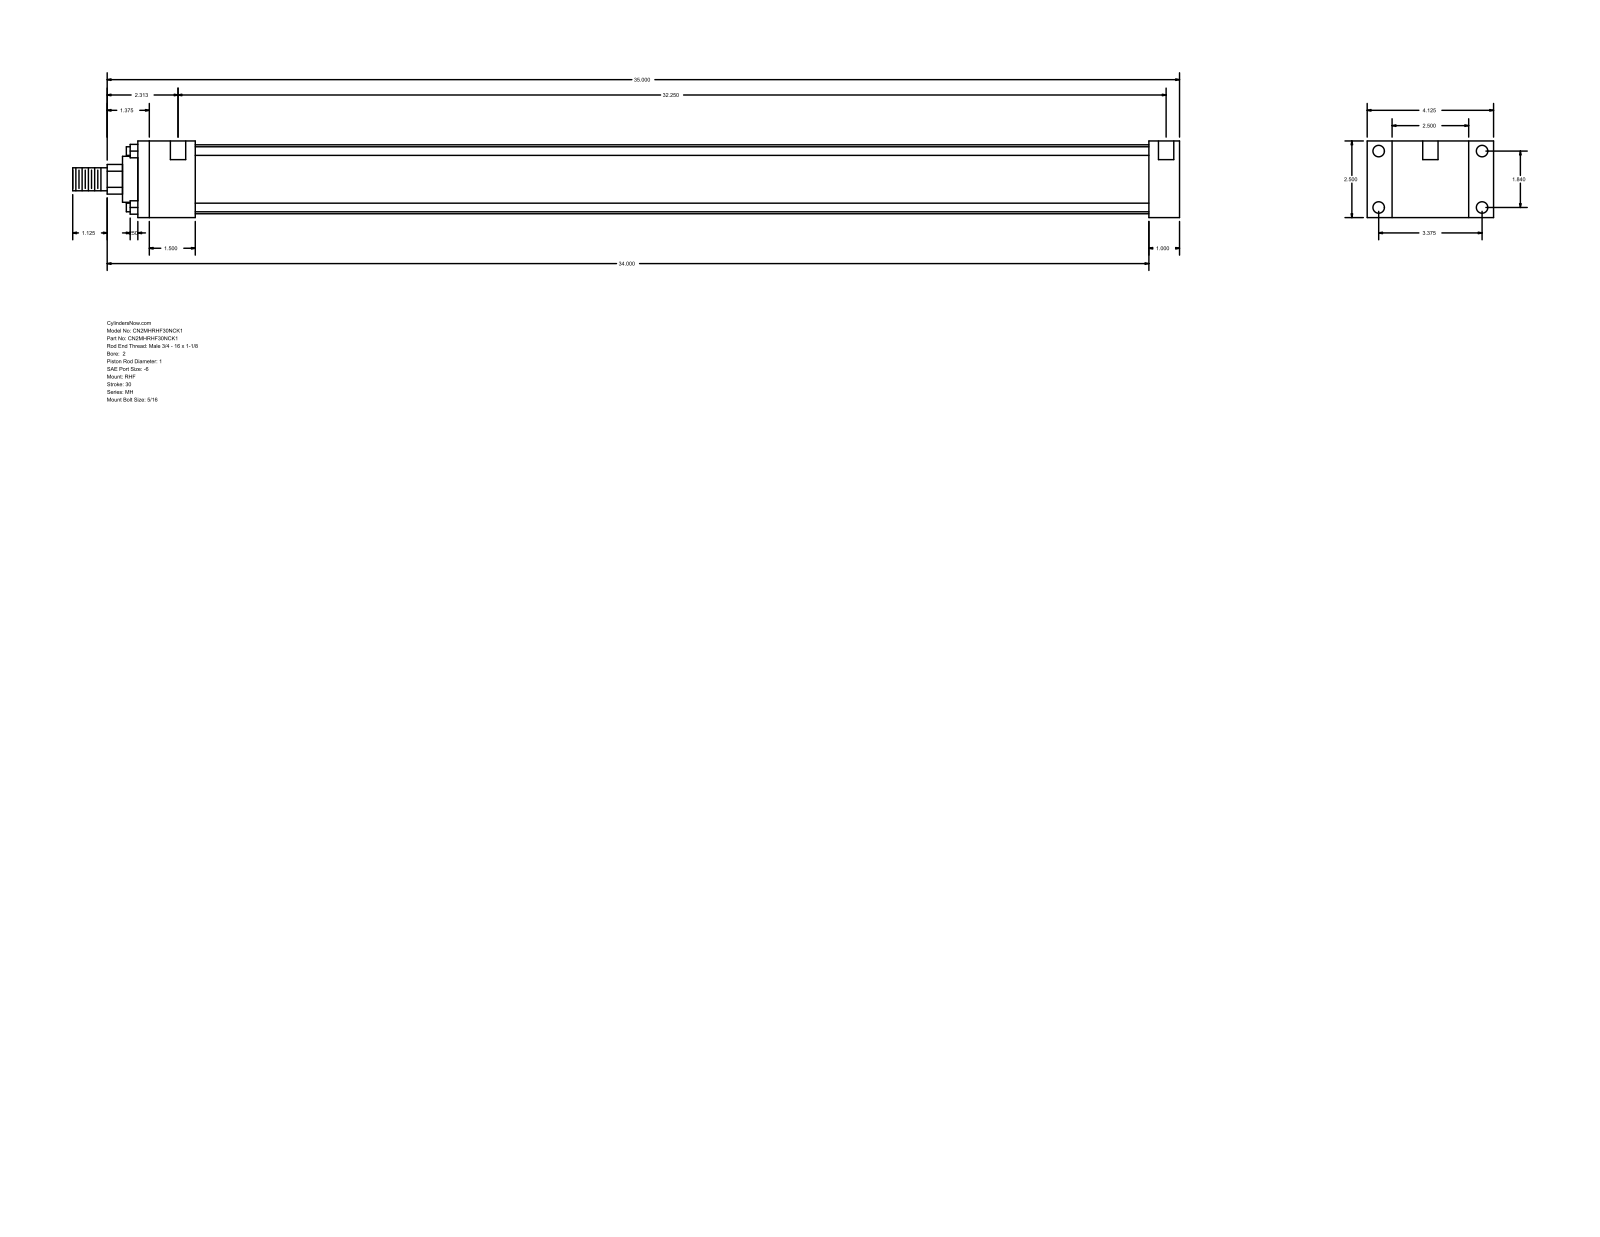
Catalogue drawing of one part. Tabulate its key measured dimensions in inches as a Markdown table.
| quantity | value |
| --- | --- |
| part name | MH_RHF__0200_1 |
| STEP written by | GSSL Pune (CONFIG_CONTROL_DESIGN) |
| units | inches |
| bodies | 0 solids, 88 faces (60 planar, 28 cylindrical, 0 other) |
| overall size | 36.125 × 4.125 × 2.5 |
| round holes (diameter × count) | 0.219 × 4, 0.375 × 4, 0.5 × 2 |
| round bosses / shafts (diameter × count) | 0.281 × 4, 2.25 × 1, 1.5 × 1, 1 × 1, 0.75 × 1 |
| partial cylindrical surfaces (radius × count) | 0.484 × 1 |
| main face-to-face distances | 2.5, 1, 0.813, 3.313, 34, 33, 4.125, 1.875, 31.125, 32.125 |
| hole center spacings | 1.84, 3.375, 3.844, 32.562, 0.125, 0.187, 32.25, 32.375 |
